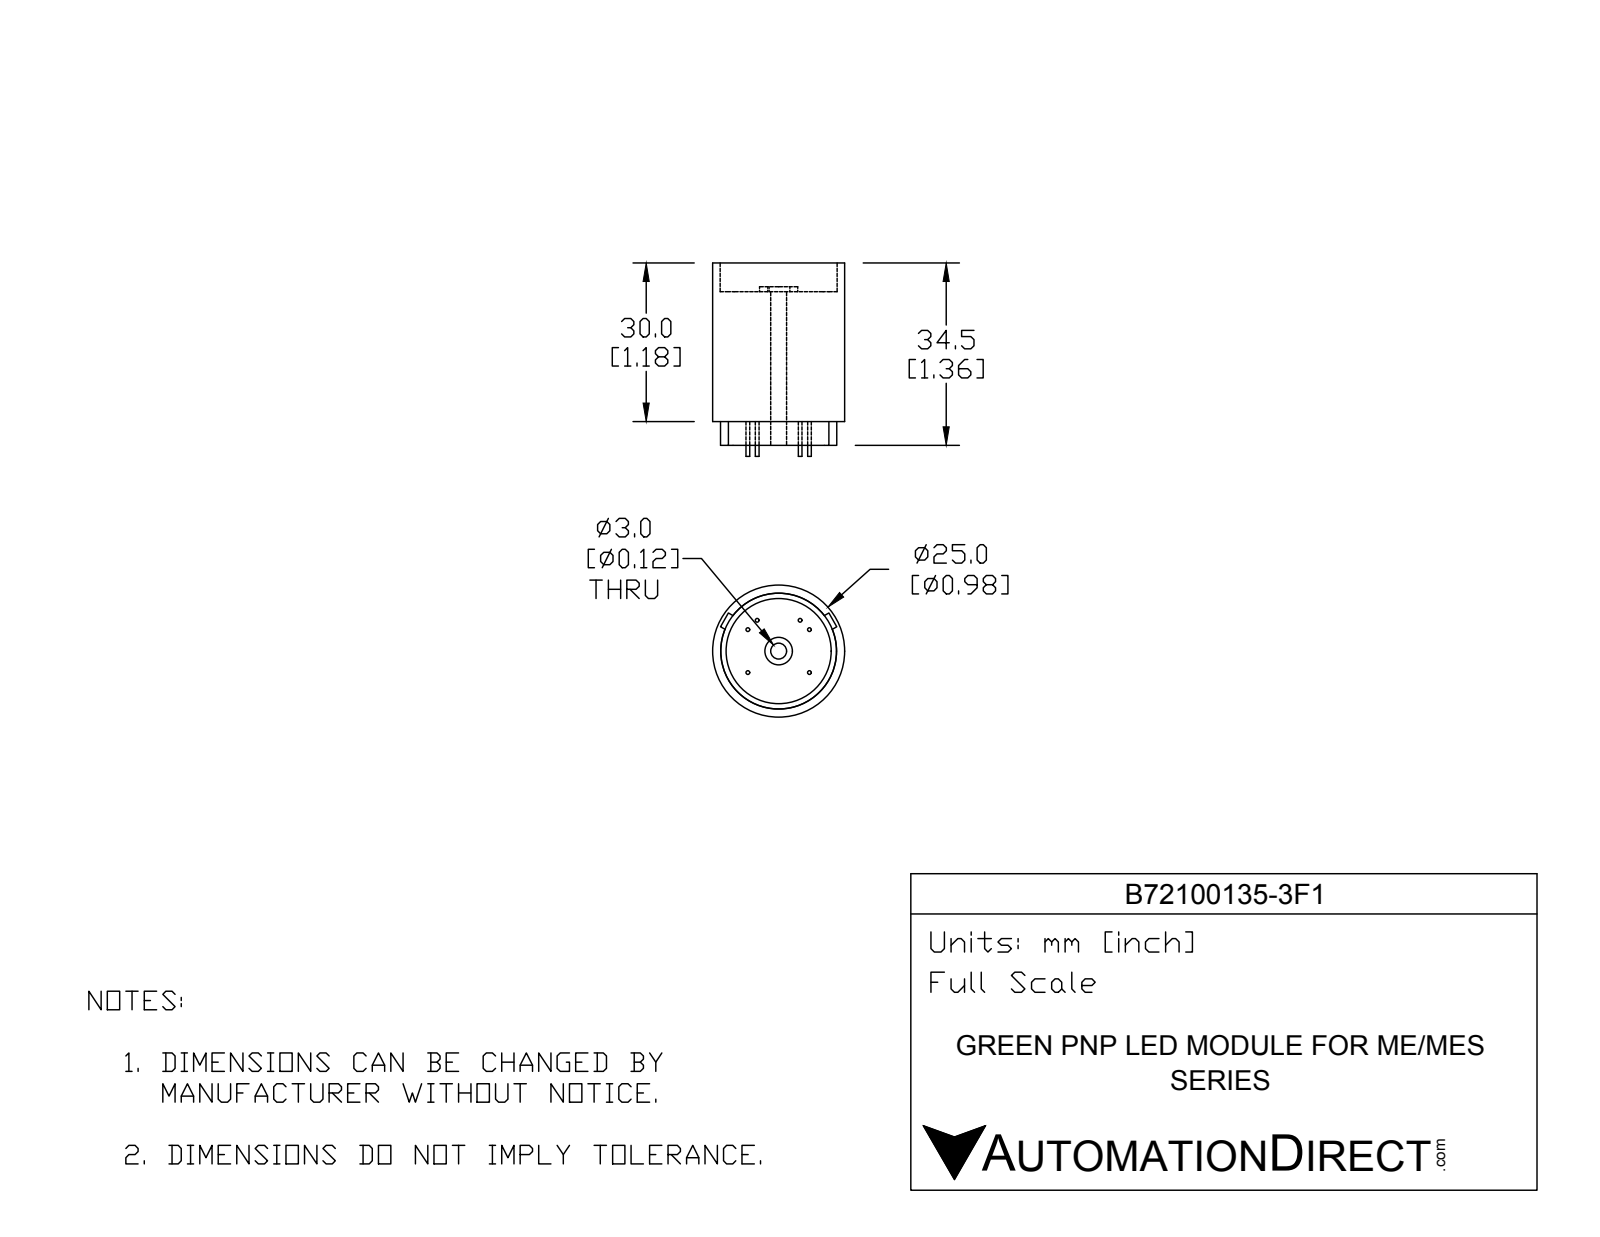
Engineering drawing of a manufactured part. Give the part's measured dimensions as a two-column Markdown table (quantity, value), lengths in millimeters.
| quantity | value |
| --- | --- |
| part name | B72100135-3F1 |
| STEP written by | SolidWorks 2016 (AUTOMOTIVE_DESIGN) |
| units | millimeters |
| bodies | 9 solids, 69 faces (36 planar, 33 cylindrical, 0 other) |
| overall size | 36.6 × 25 × 25 |
| volume | 12 963 mm³ |
| surface area | 4 884 mm² |
| round holes (diameter × count) | 3 × 1, 4.22 × 1, 19.9 × 1, 21.5 × 1 |
| round bosses / shafts (diameter × count) | 0.7 × 6, 25 × 1, 21.9 × 1, 7.22 × 1, 5.2 × 1 |
| main face-to-face distances | 24.56, 30, 5.44, 4.5, 29.06, 34.5, 25.5, 0.94, 3.05, 3.1 |
